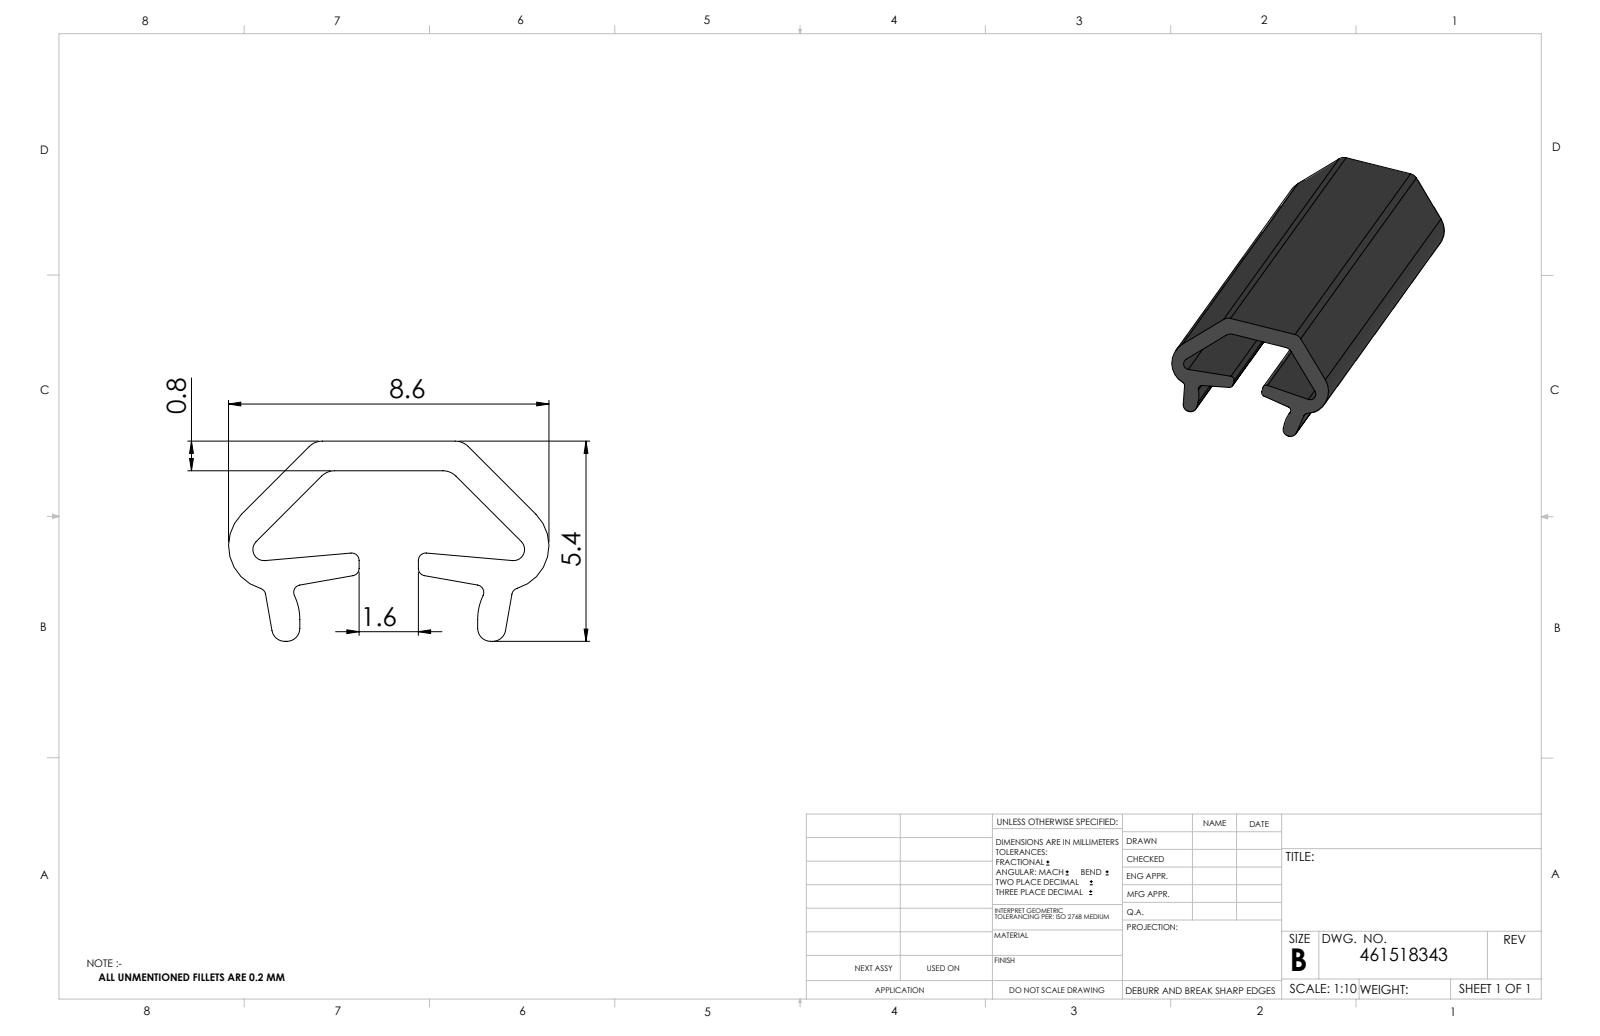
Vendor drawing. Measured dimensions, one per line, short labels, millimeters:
name: 461518343_c_1
written by: SolidWorks 2014 (CONFIG_CONTROL_DESIGN)
unit: mm
bodies: 1 solid, 44 faces (20 planar, 24 cylindrical, 0 other)
size: 2000 × 8.65 × 5.4
volume: 30 740 mm³; area: 82 178 mm²
rounds: 8× R0.2, 4× R0.35, 4× R0.5, 2× R0.3, 2× R1.2, 2× R1.5
face distances: 0.8, 1.6, 3.2, 4.8, 5.4, 4.6, 2000
